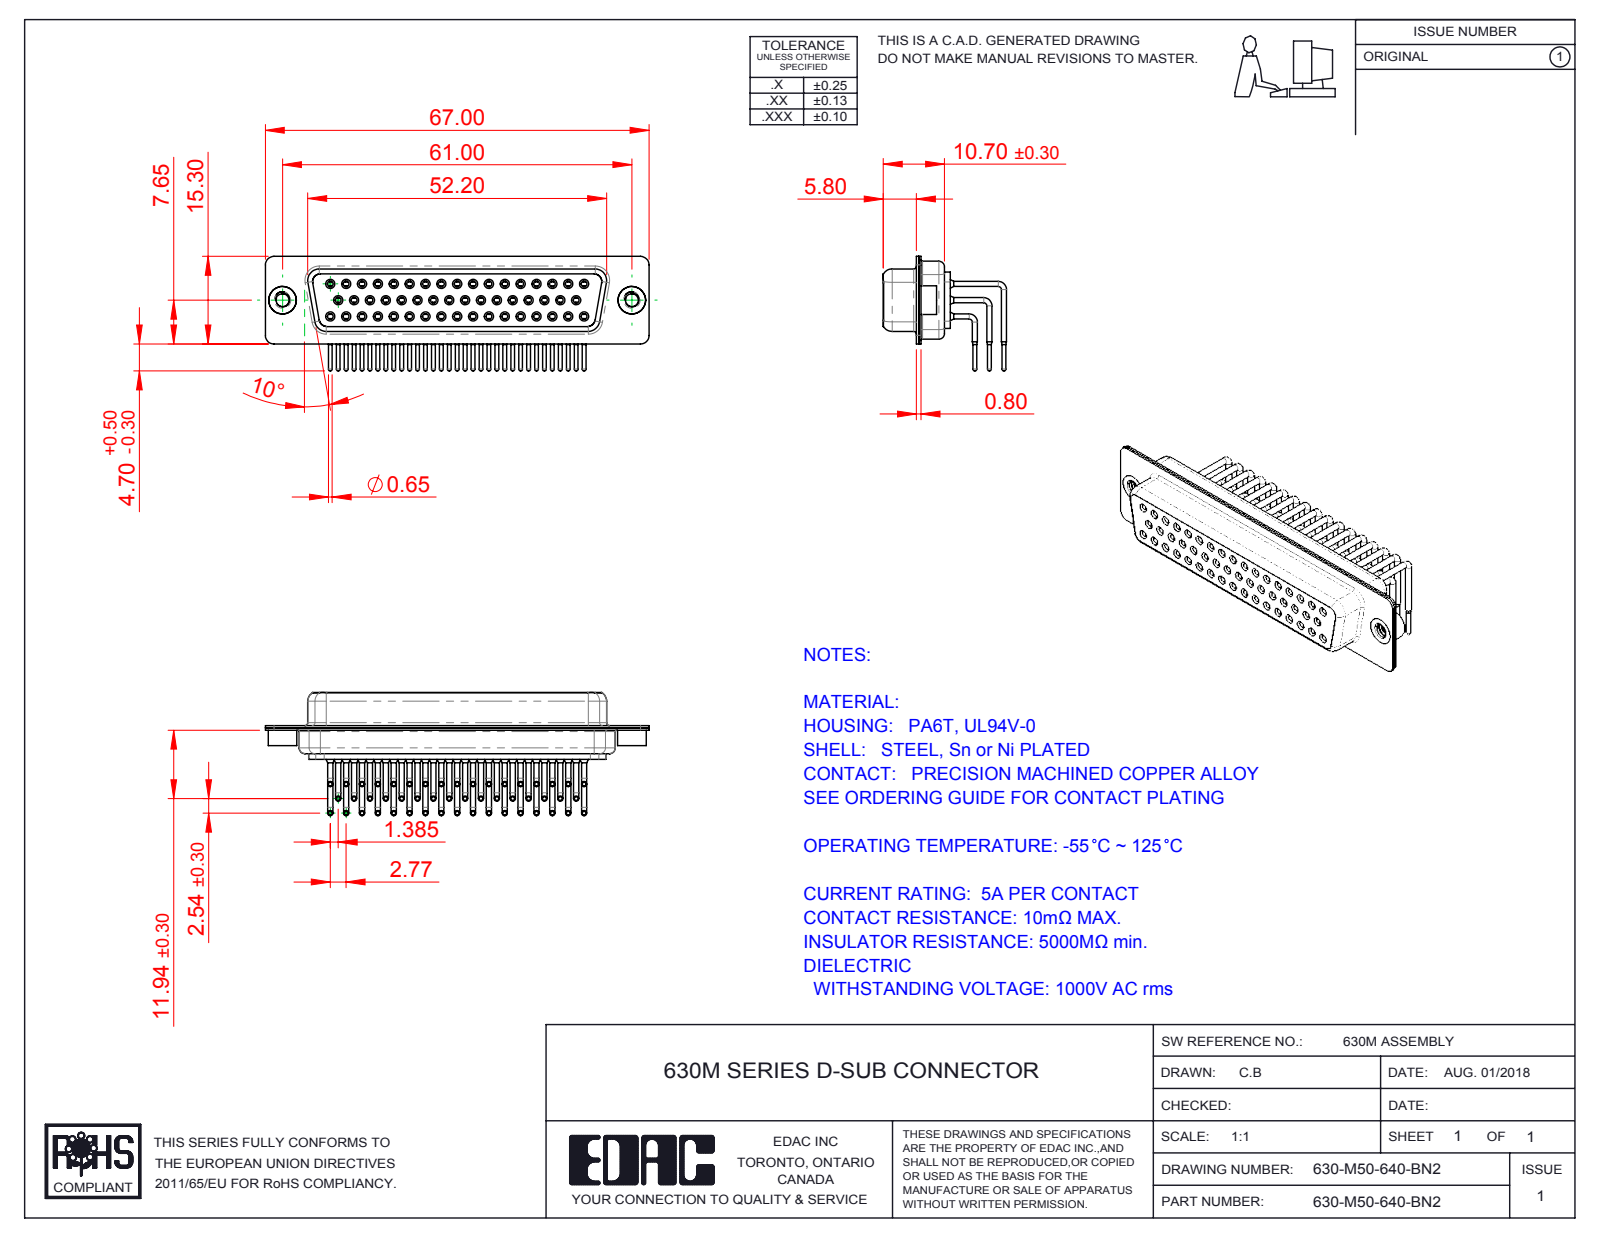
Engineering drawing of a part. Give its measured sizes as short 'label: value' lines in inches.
name: 630M Shell Front_50 Contacts; 630M Shell Rear_50 Contacts; 630M Contact Row 1_50 Contacts; 630M Housing_50 Contacts (+4 more)
written by: SolidWorks 2016 (CONFIG_CONTROL_DESIGN)
unit: in
bodies: 55 solids, 2929 faces (817 planar, 1287 cylindrical, 825 other)
size: 2.638 × 0.848 × 0.787
volume: 0.428 in³; area: 25.67 in²
holes: 50× ⌀0.039, 50× ⌀0.043, 50× ⌀0.067, 50× ⌀0.071, 50× ⌀0.079, 2× ⌀0.089, 2× ⌀0.157, 2× ⌀0.189
bosses: 100× ⌀0.035, 50× ⌀0.063, 50× ⌀0.059, 50× ⌀0.026, 2× ⌀0.197, 2× ⌀0.193
rounds: 16× R0.059, 12× R0.079, 8× R0.053, 8× R0.063, 4× R0.01, 4× R0.02, 4× R0.024, 4× R0.026
face distances: 0.016, 0.053, 0.467, 0.033, 0.087, 0.217, 0.482, 0.232, 0.413, 0.031
hole spacings: 0.109, 0.124, 0.218, 0.327, 0.436, 0.545, 0.654, 0.763
